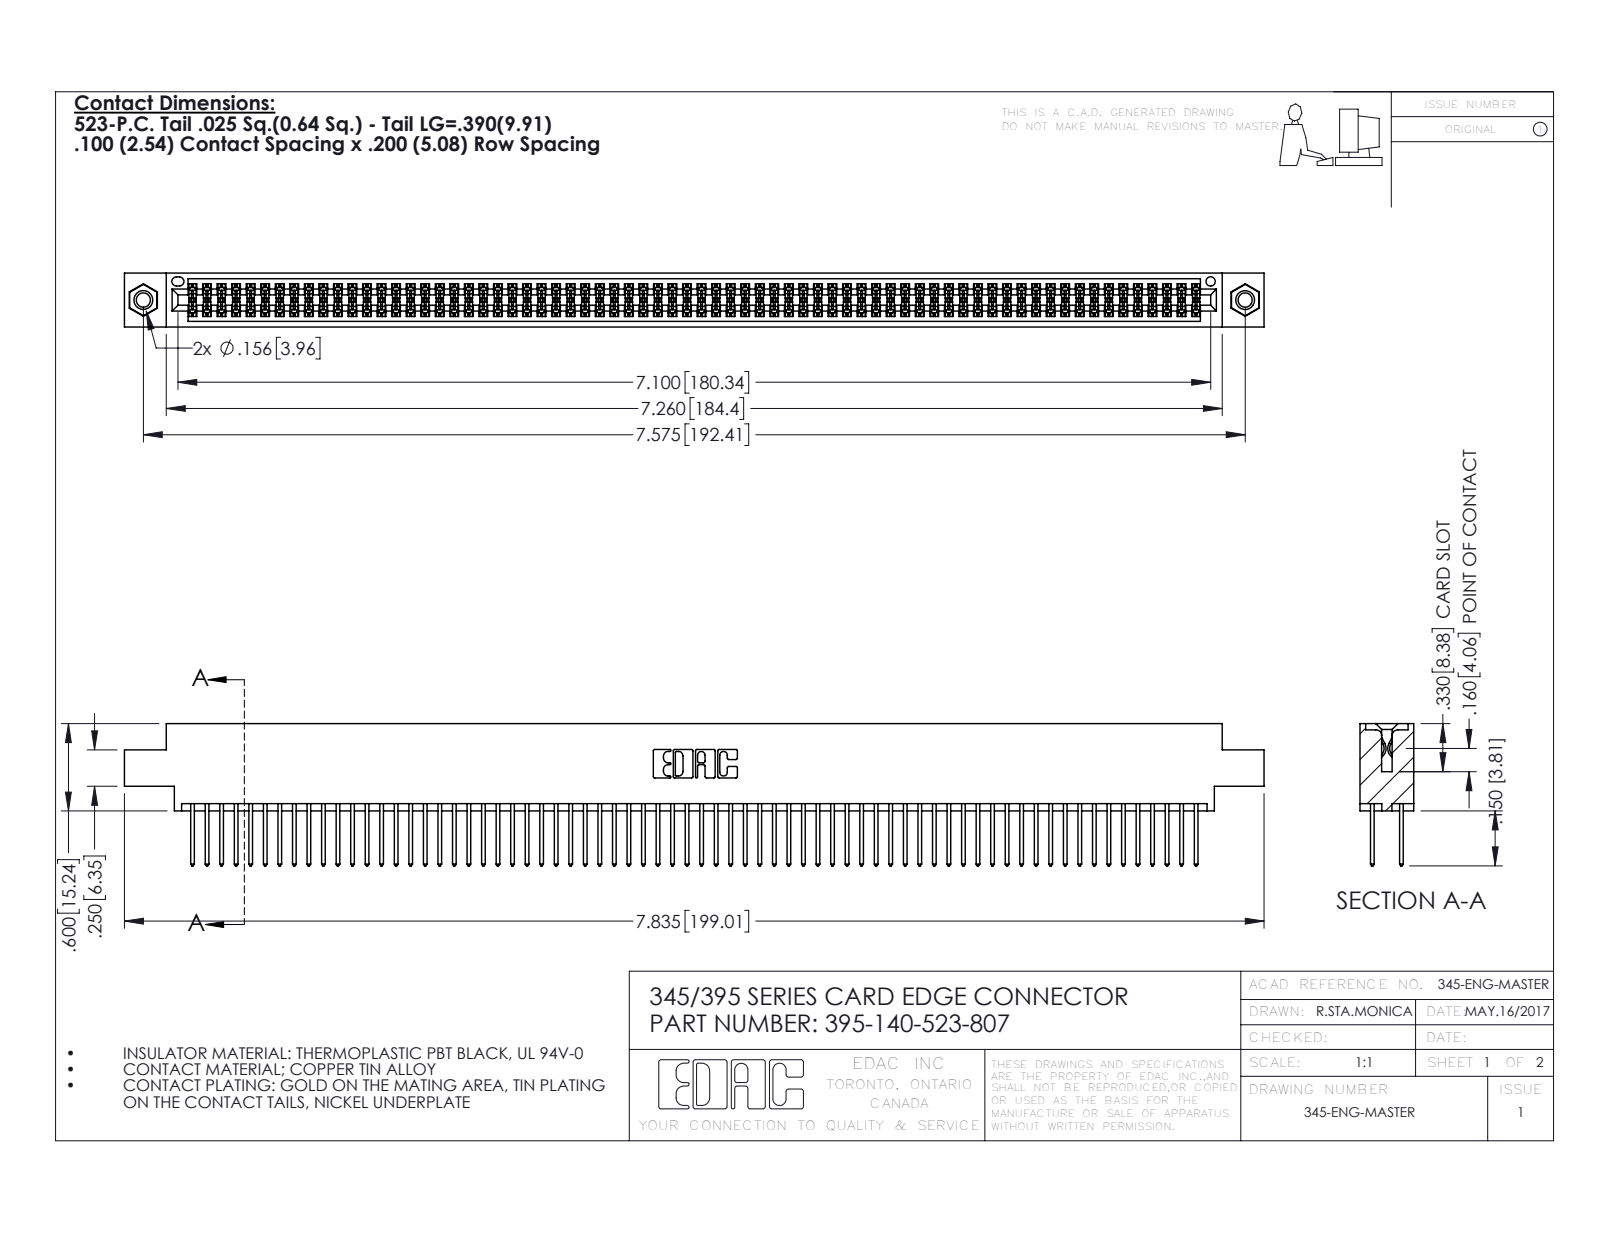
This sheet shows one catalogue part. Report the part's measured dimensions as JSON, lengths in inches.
{"part_name": "395-140-523-807; 345 Part_0.170 Offset - 0.156 Dia-TI; 345-250-001_345-250-005-103; 345-292-001_345-293-123", "step_written_by": "SolidWorks 2016 (CONFIG_CONTROL_DESIGN)", "units": "inches", "bodies": {"solids": 143, "faces": 7190, "planar": 4736, "cylindrical": 2438, "other": 16}, "overall_size": [7.835, 0.977, 0.37], "volume_in3": 1.205, "surface_area_in2": 48.36, "round_holes": [[0.098, 2], [0.125, 2], [0.156, 2], [0.064, 1]], "round_bosses_or_shafts": [[0.155, 2]], "partial_cylinders_radius": [[0.006, 210], [0.01, 140], [0.01, 22], [0.007, 6], [0.031, 6], [0.026, 3], [0.014, 2], [0.019, 2]], "face_to_face_distances": [0.072, 0.298, 0.2, 0.098, 0.272, 0.025, 0.37, 0.225, 0.175, 0.149], "hole_center_spacings": [0.27, 7.339, 7.575]}
